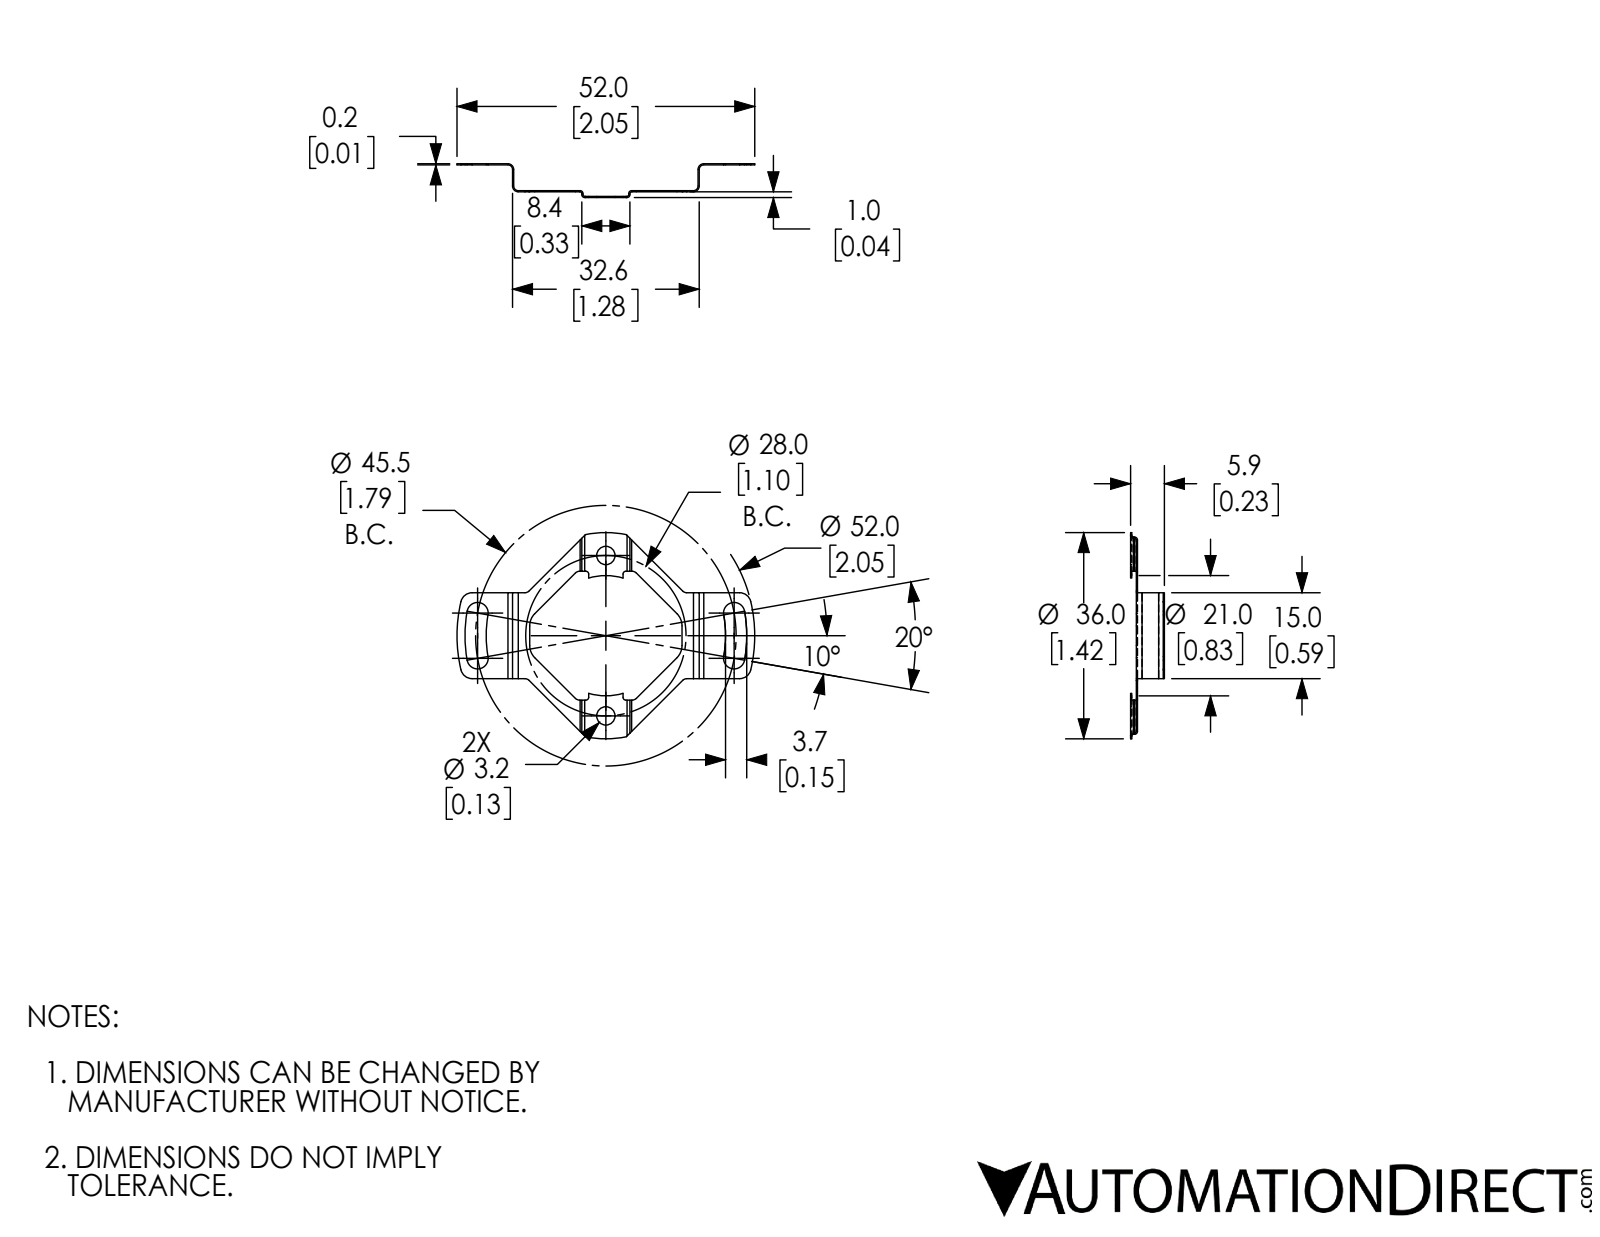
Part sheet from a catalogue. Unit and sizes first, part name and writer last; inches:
Units: inches
Overall size (bounding box): 2.047 × 1.417 × 0.232
Round holes (diameter × count): ⌀0.126 ×2
Partial cylindrical surfaces — rounded edges, fillets, slot ends (radius × count): R0.039 ×12, R0.02 ×8, R0.012 ×4, R0.031 ×4, R0.073 ×4, R0.079 ×4, R0.118 ×4, R0.413 ×1
Main face-to-face distances: 0.185, 0.039, 0.224, 0.177, 0.193, 0.047, 0.217, 0.031, 0.232, 1.276
Hole centre spacings: 1.102
Volume: 0.009 in³ · Surface area: 2.298 in²
Bodies: 1 solid, 111 faces (46 planar, 65 cylindrical, 0 other)
Part name (STEP PRODUCT): TRD-SHR-45
STEP written by: SolidWorks 2017 (AUTOMOTIVE_DESIGN)
